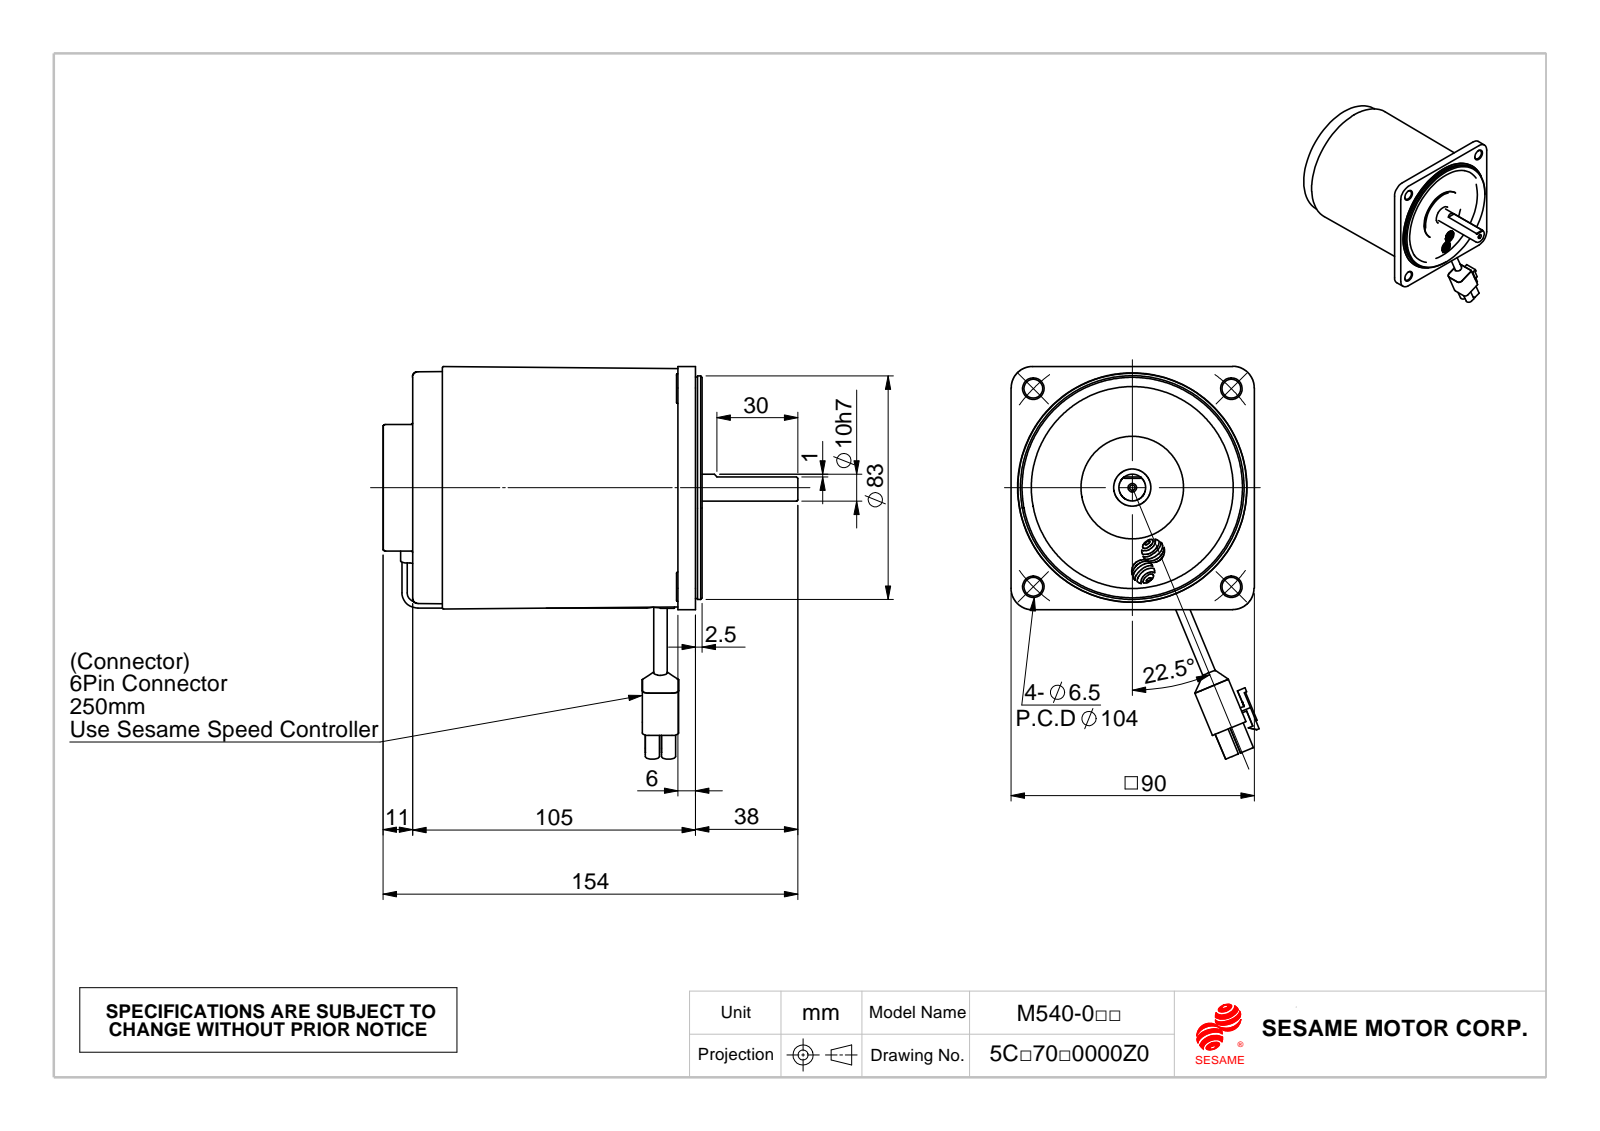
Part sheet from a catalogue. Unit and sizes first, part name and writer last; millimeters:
Units: millimetres
Overall size (bounding box): 154 × 145.78 × 92.07
Round holes (diameter × count): ⌀3.8 ×4, ⌀5.5 ×4, ⌀7 ×4, ⌀2.5 ×3, ⌀2 ×2, ⌀3.1 ×2, ⌀7.2 ×1, ⌀9.5 ×1, ⌀10 ×1, ⌀13.7 ×1, ⌀21 ×1, ⌀24 ×1
Round bosses / shafts (diameter × count): ⌀2 ×2, ⌀84.22 ×1, ⌀83 ×1, ⌀82.2 ×1, ⌀58 ×1, ⌀47 ×1, ⌀46 ×1, ⌀38 ×1
Partial cylindrical surfaces — rounded edges, fillets, slot ends (radius × count): R0.5 ×14, R0.25 ×8, R0.78 ×8, R1.5 ×8, R1.66 ×8, R2.92 ×8, R2.5 ×7, R1 ×6
Main face-to-face distances: 102.4, 7.3, 95.1, 1, 103.5, 96.1, 103.4, 102.5, 7.4, 1.5
Hole centre spacings: 6, 3.6, 4.24, 5.01, 38.18, 52, 73.18, 73.54
Volume: 724 379 mm³ · Surface area: 79 458 mm²
Bodies: 8 solids, 545 faces (154 planar, 279 cylindrical, 112 other)
Part name (STEP PRODUCT): 油封10x26x5; 線扣; M540-R; 40A (+1 more)
STEP written by: SolidWorks 2010 (CONFIG_CONTROL_DESIGN)
